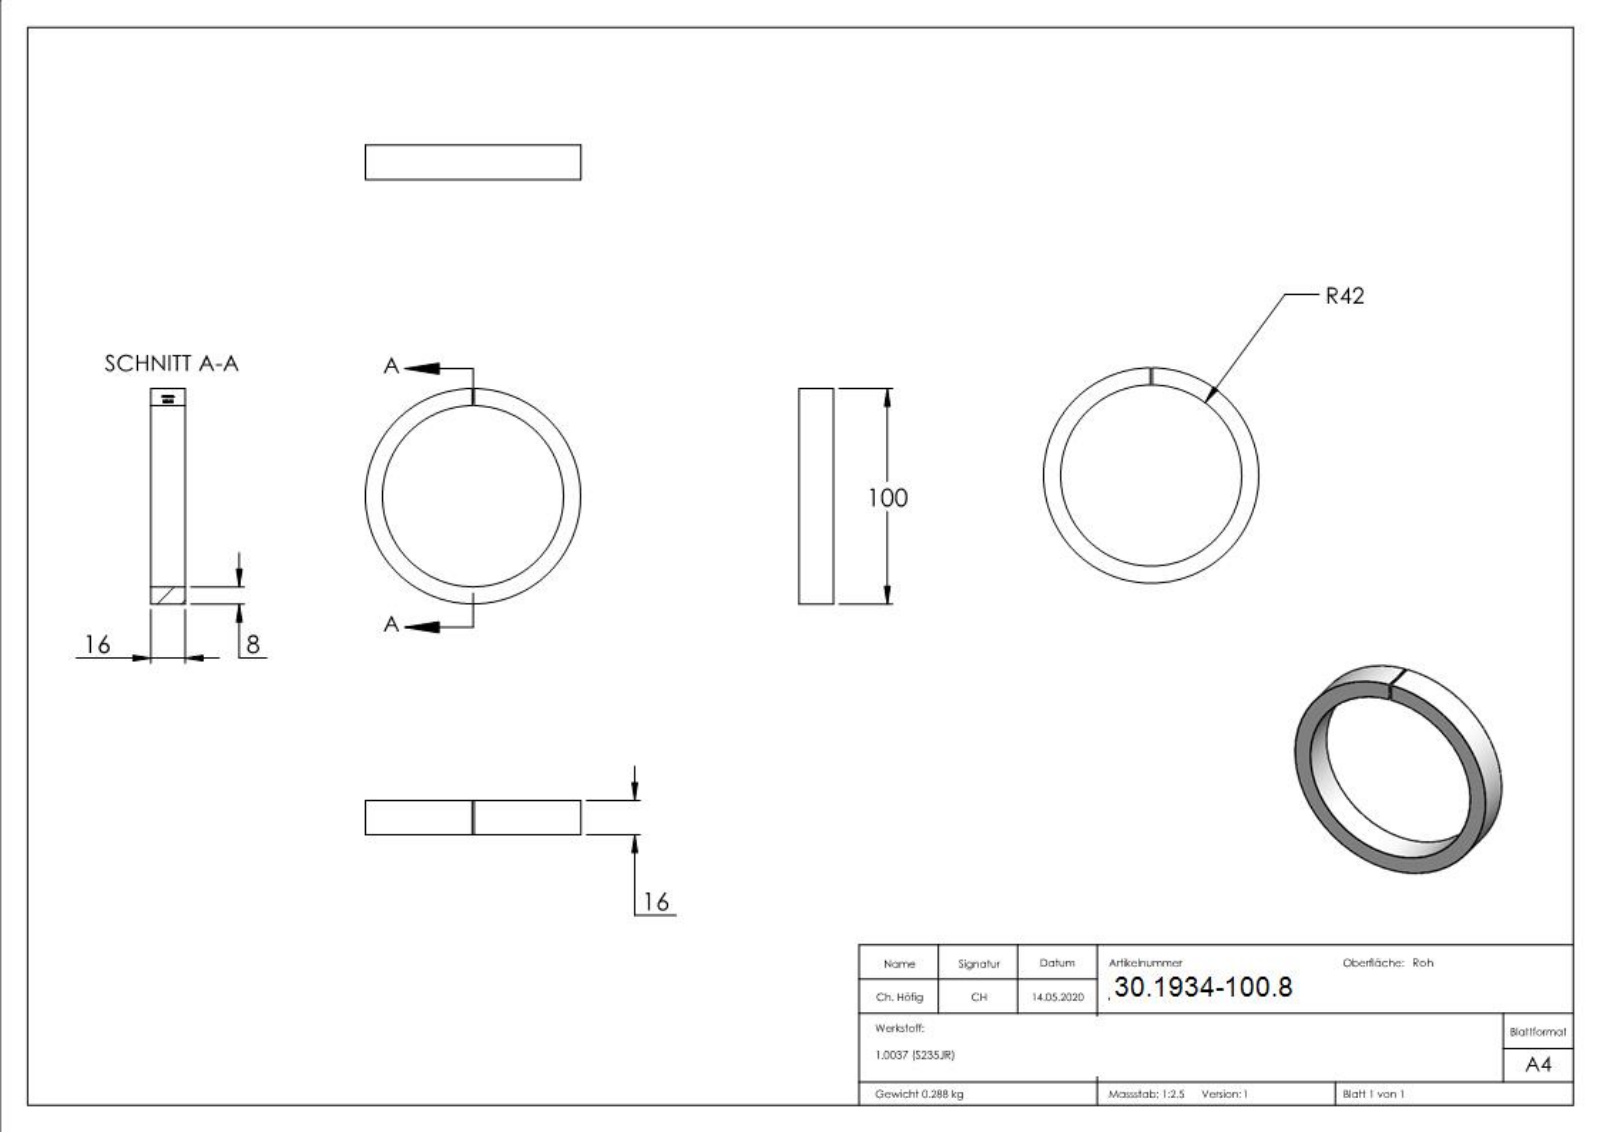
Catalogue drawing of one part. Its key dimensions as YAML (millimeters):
part_name: "5638-100"
step_written_by: "SolidWorks 2015 (CONFIG_CONTROL_DESIGN)"
units: millimeters
bodies: {solids: 1, faces: 220, planar: 104, cylindrical: 2, other: 114}
overall_size: [100, 100, 16]
volume: 36867
surface_area: 14087
round_holes:
  - {diameter: 84, count: 1}
round_bosses_or_shafts:
  - {diameter: 100, count: 1}
face_to_face_distances: [16, 1, 1.1, 1.78, 0.83, 2.12, 0.99, 2.77, 1.21, 3.33]
